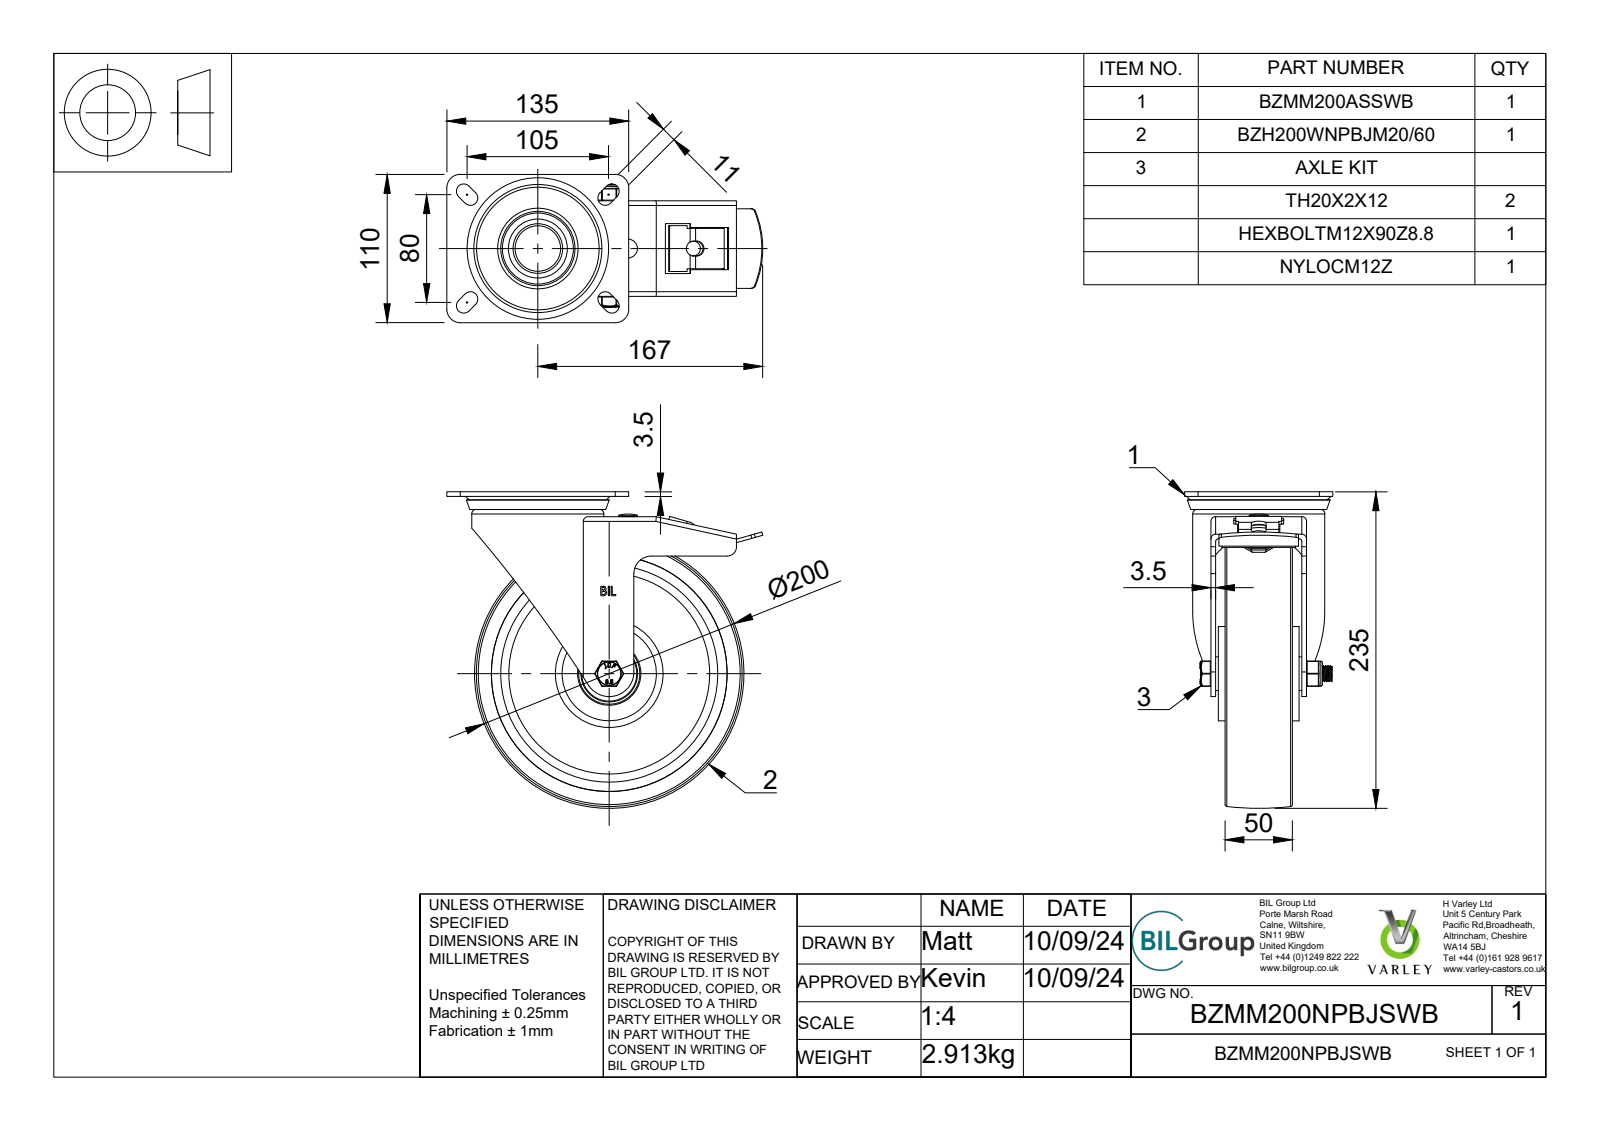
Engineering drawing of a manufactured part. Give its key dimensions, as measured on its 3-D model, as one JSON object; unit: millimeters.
{"part_name": "BZMM200NPBJSWB v3; BZMM200ASSWB - 64 v1; ZINC PLATED, PRESSED STEEL TOP PLATE; ZINC PLATED, PRESSED STEEL TOP PLATE Geometry (+7 more)", "step_written_by": "Autodesk Translation Framework v13.14.0.145 (AUTOMOTIVE_DESIGN)", "units": "millimeters", "bodies": {"solids": 82, "faces": 1277, "planar": 549, "cylindrical": 248, "other": 480}, "overall_size": [235, 234.5, 110], "volume_mm3": 1065000, "surface_area_mm2": 379871, "round_holes": [[8, 1], [11, 1], [12, 1], [12.2, 1], [14, 1], [20, 1], [28.5, 1], [30.8, 1], [33.75, 1], [40, 1], [40.3, 1], [40.5, 1]], "round_bosses_or_shafts": [[98, 1], [78, 1], [70, 1], [50, 1], [40.8, 1], [39.75, 1], [31.3, 1], [27, 1]], "partial_cylinders_radius": [[0.5, 19], [5.5, 10], [1.75, 7], [0.25, 6], [2.5, 6], [0.47, 4], [0.9, 4], [3.5, 4]], "face_to_face_distances": [3.5, 22, 28, 7, 5.5, 6, 13, 32.5, 9, 29], "hole_center_spacings": [67]}
